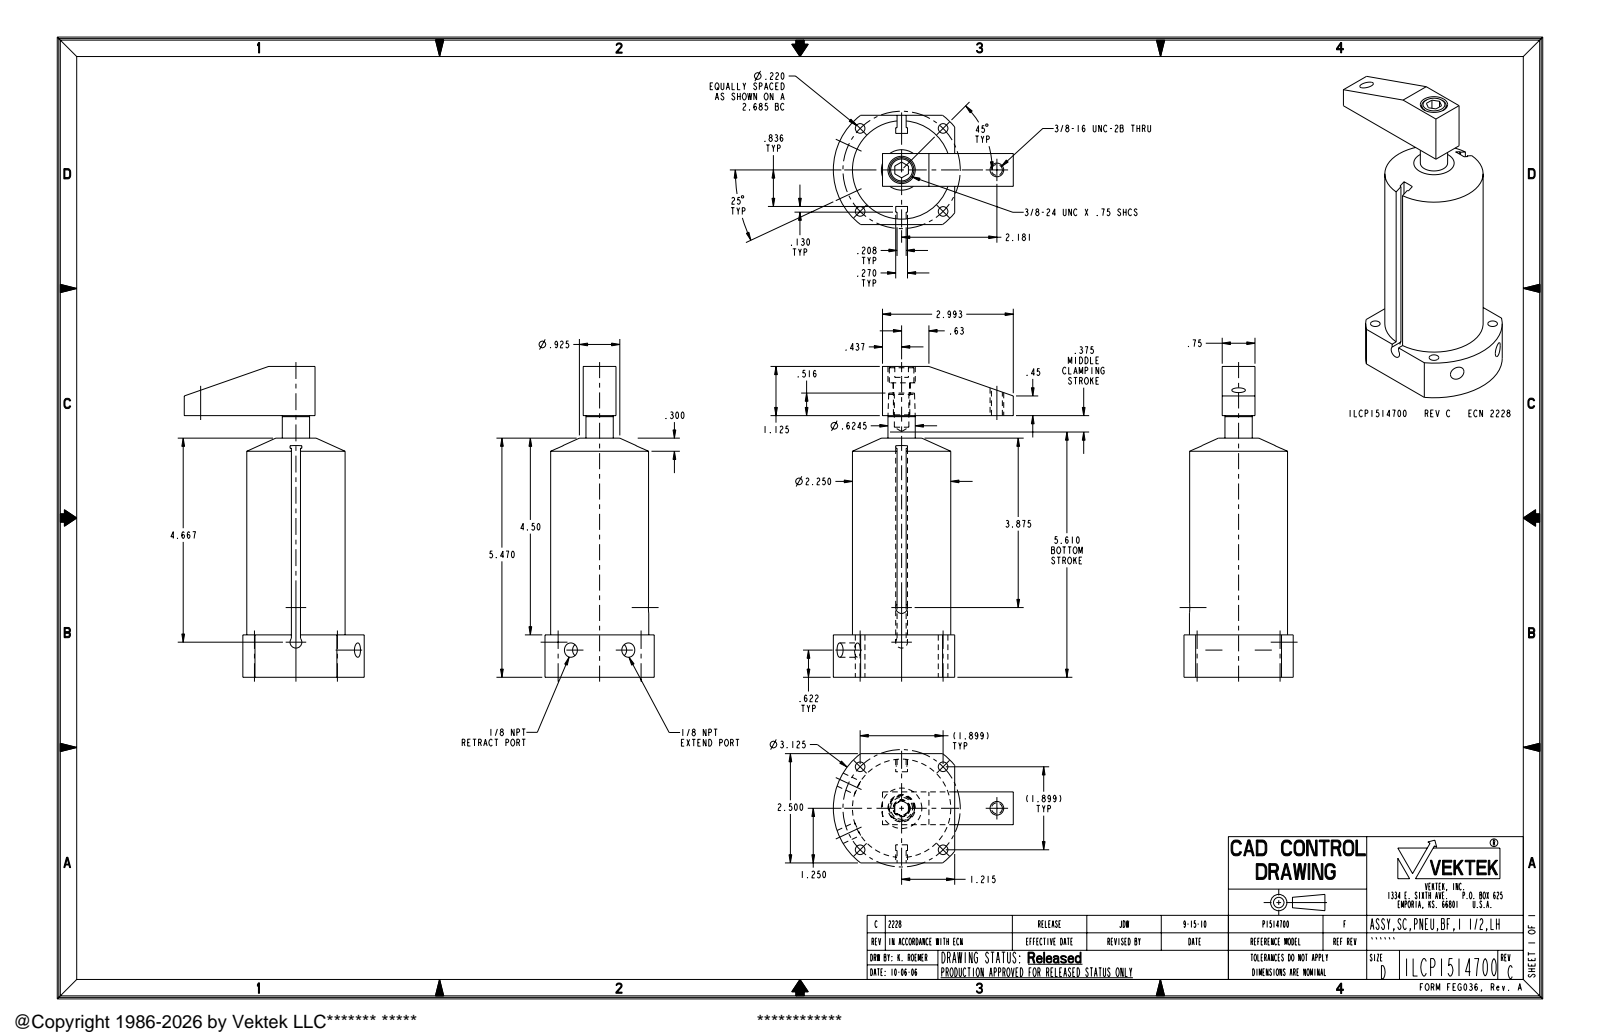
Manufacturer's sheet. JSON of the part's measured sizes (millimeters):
{"part_name": "ILCP1514700; ILC91501503; ILCP1514700_ASM", "step_written_by": "PRO/ENGINEER BY PARAMETRIC TECHNOLOGY CORPORATION, 2007460 (AUTOMOTIVE_DESIGN_CC2)", "units": "millimeters", "bodies": {"solids": 2, "faces": 91, "planar": 43, "cylindrical": 36, "other": 12}, "overall_size": [180.6, 104.6, 63.5], "volume_mm3": 405900, "surface_area_mm2": 51450, "round_holes": [[5.6, 4], [8.3, 2], [7.9, 1], [8.4, 1], [9.9, 1], [15.9, 1]], "round_bosses_or_shafts": [[57.2, 1], [15.8, 1], [14.3, 1], [9.5, 1], [6.4, 1]], "partial_cylinders_radius": [[3.4, 2], [39.7, 1]], "face_to_face_distances": [22.2, 41.3, 19.1, 10.5, 53, 11.7, 30.7, 24.6, 0.8, 6.1], "hole_center_spacings": [34.1, 48.2, 39.5, 68.2, 83.1, 55.4]}
